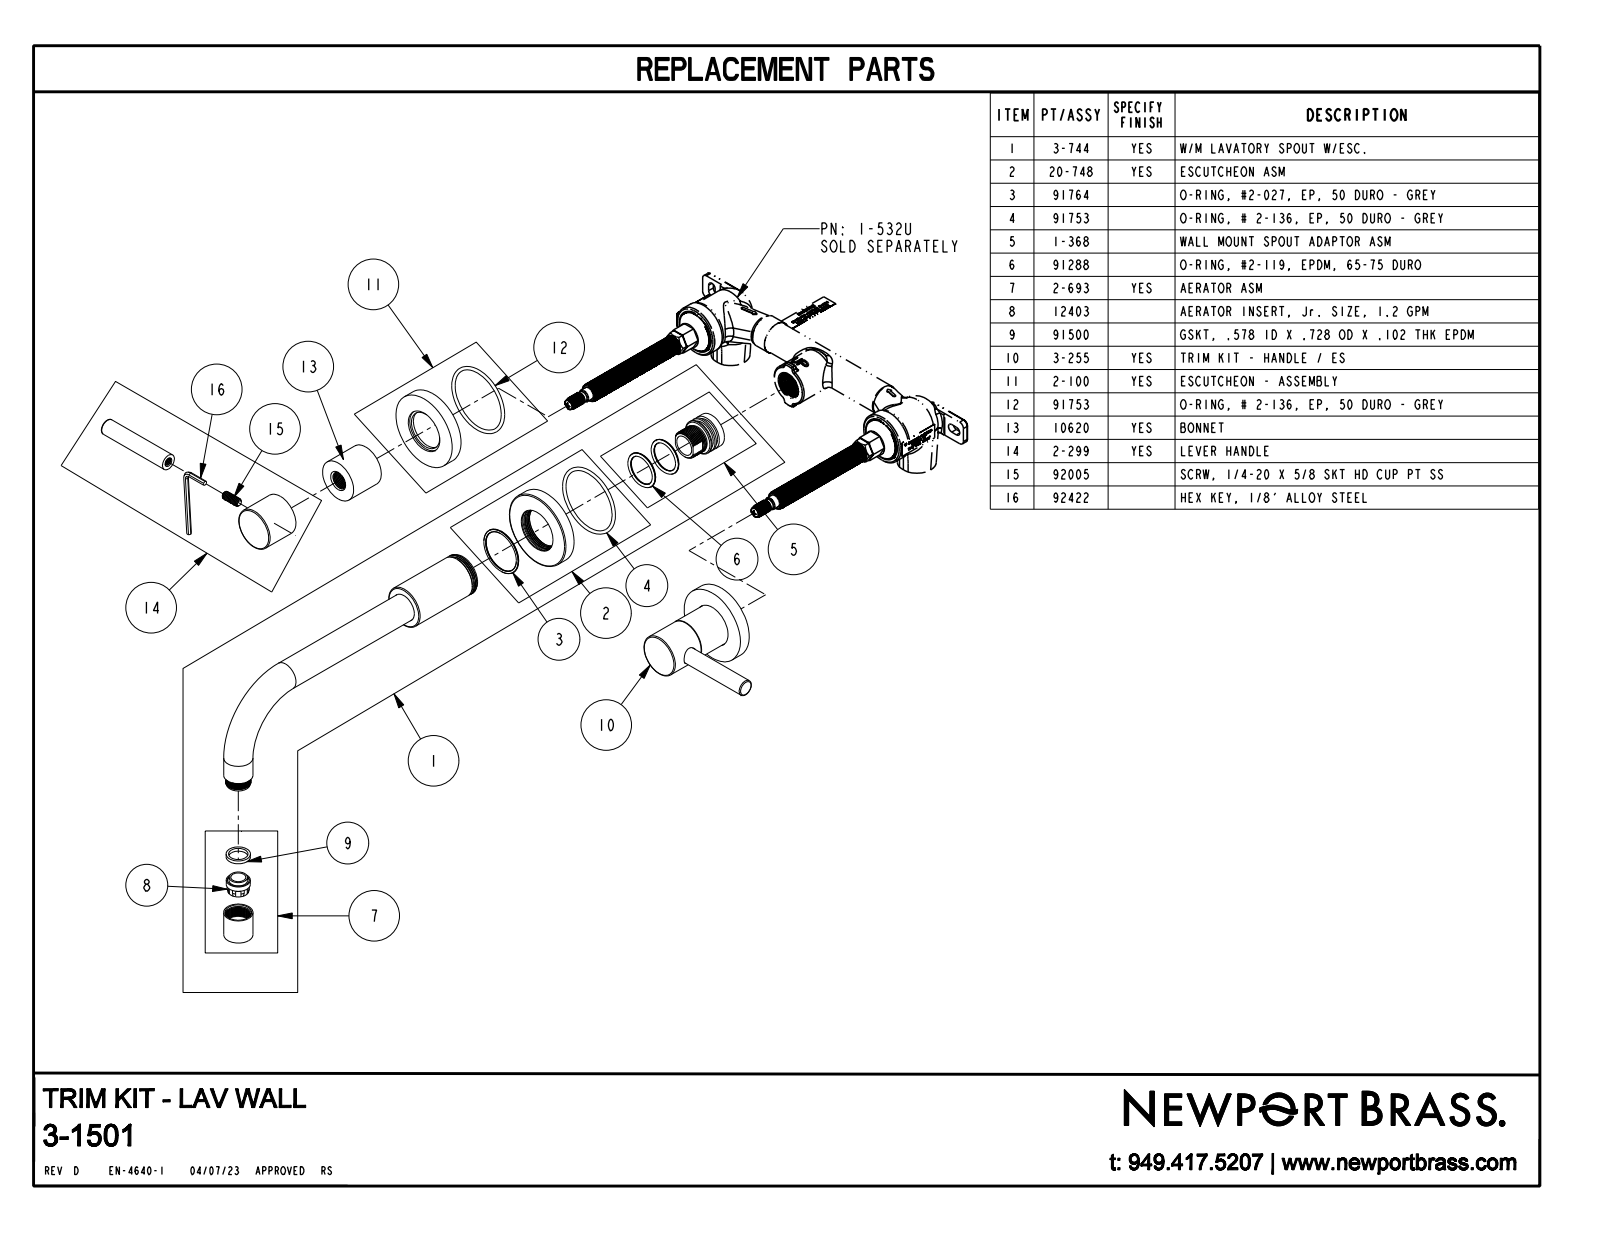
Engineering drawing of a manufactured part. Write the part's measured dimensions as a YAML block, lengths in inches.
part_name: "3-1501_SW0002"
step_written_by: "CREO PARAMETRIC BY PTC INC, 2018400 (CONFIG_CONTROL_DESIGN)"
units: inches
bodies: {solids: 5, faces: 54, planar: 16, cylindrical: 24, other: 14}
overall_size: [14.013, 9.937, 4.627]
volume: 20.57
surface_area: 101
round_bosses_or_shafts:
  - {diameter: 2.375, count: 3}
  - {diameter: 1.312, count: 3}
  - {diameter: 1.313, count: 2}
  - {diameter: 0.875, count: 2}
  - {diameter: 0.5, count: 1}
face_to_face_distances: [0.375, 1.483, 1.108, 1.503, 1.128, 0.02, 2.623, 2.248, 1.14, 1.12]
